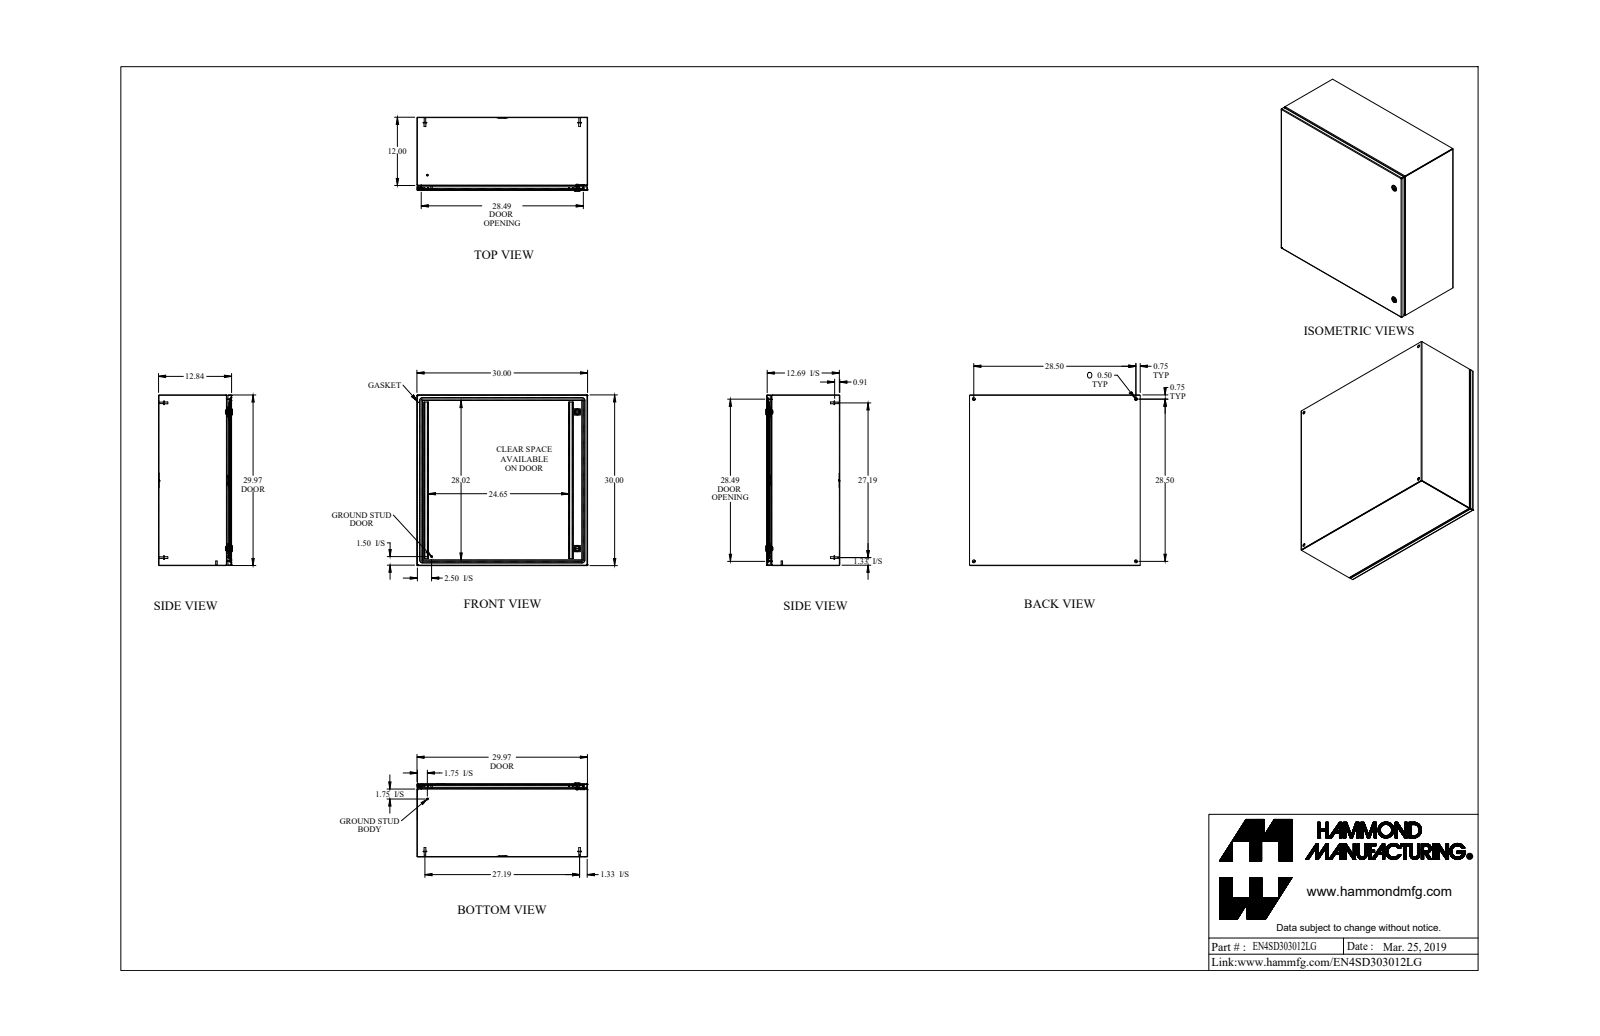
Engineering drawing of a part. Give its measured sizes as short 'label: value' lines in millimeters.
name: EN4SD303012LG
written by: SolidWorks 2019 (AUTOMOTIVE_DESIGN)
unit: mm
bodies: 33 solids, 838 faces (399 planar, 283 cylindrical, 156 other)
size: 762 × 762 × 330.1
volume: 4 346 000 mm³; area: 4 794 000 mm²
holes: 4× ⌀12.7, 2× ⌀5.9, 2× ⌀15.9, 2× ⌀19.9, 1× ⌀4.4, 1× ⌀6.1, 1× ⌀6.1
bosses: 4× ⌀15.9, 4× ⌀8, 4× ⌀6.9, 2× ⌀27.9, 2× ⌀13.3, 2× ⌀7.1, 2× ⌀6.4, 1× ⌀11.6
rounds: 14× R0.9, 14× R2.7, 12× R1.1, 12× R2.1, 12× R7.9, 8× R2.5, 6× R0.2, 6× R1.6
face distances: 1.8, 324.2, 760.2, 322.4, 326.1, 758.3, 762, 21.3, 303, 19.1
hole spacings: 723.9, 699, 1023.7, 63.3, 63.3, 609.6, 667.3, 667.3
